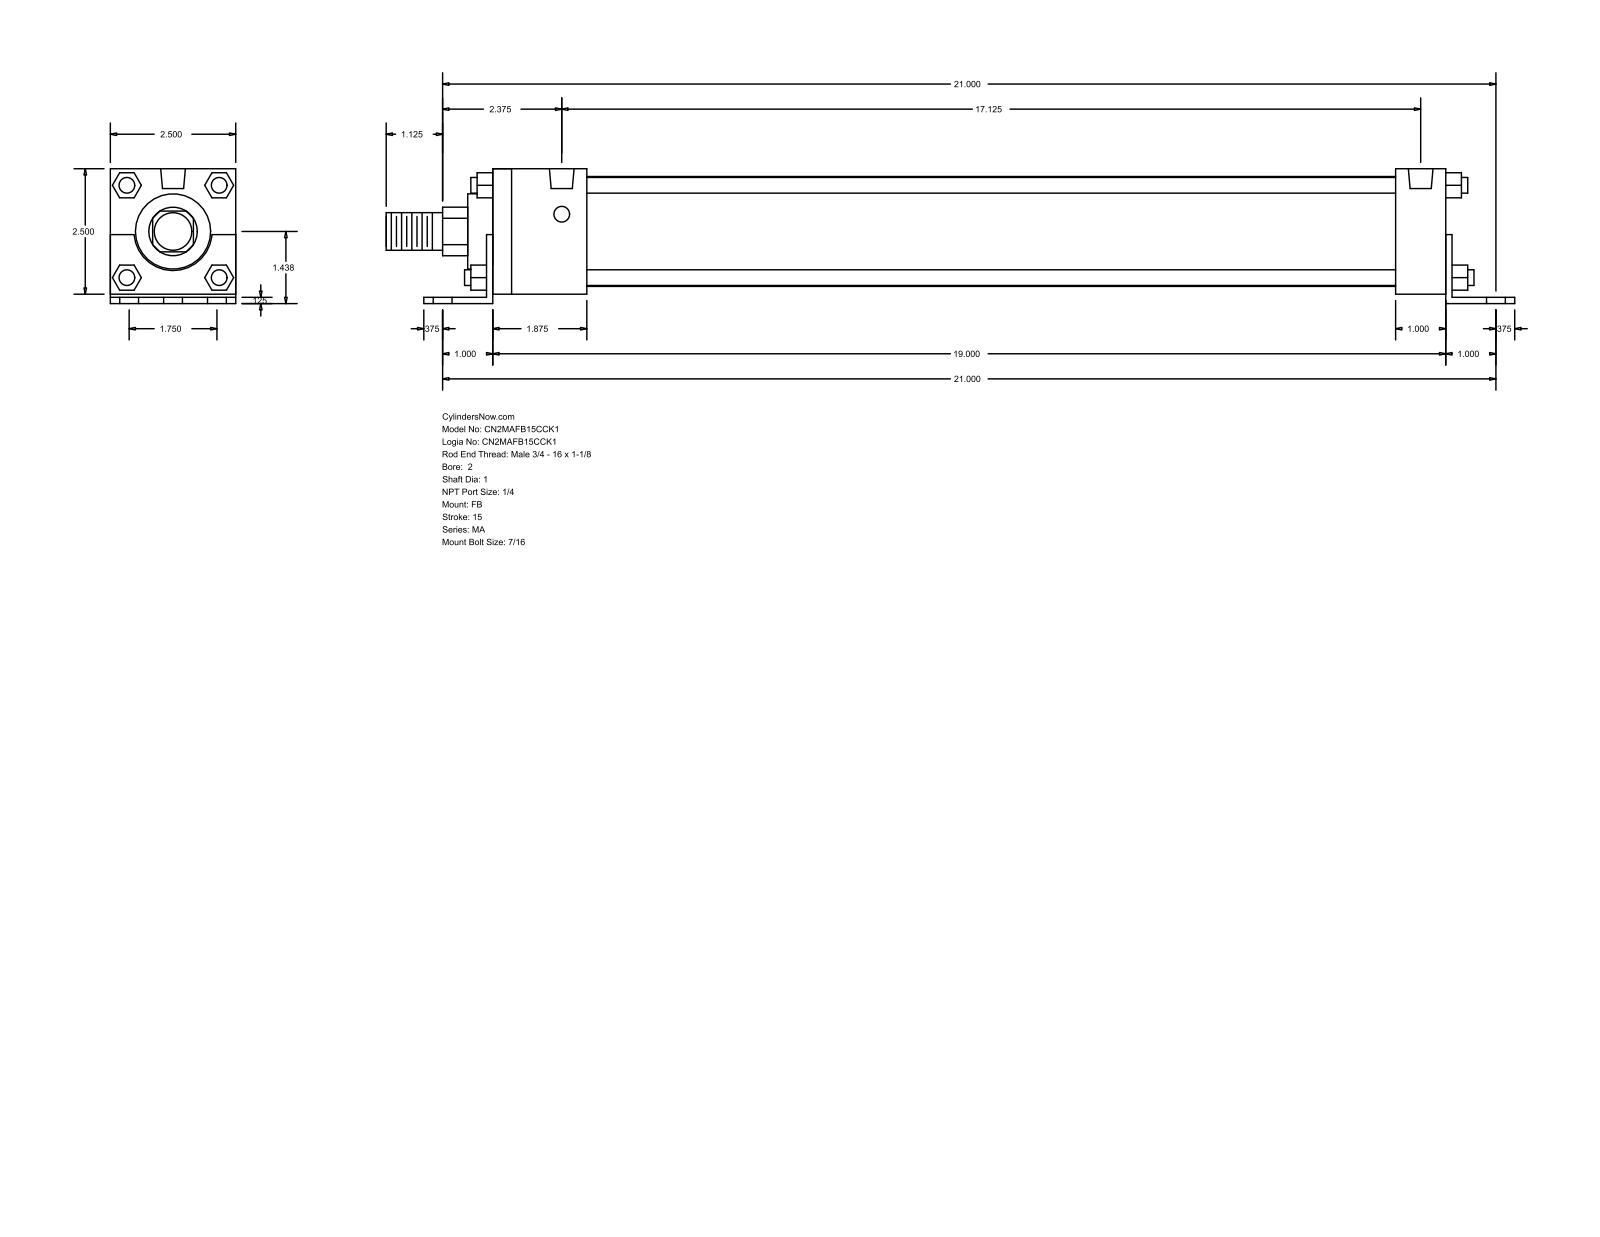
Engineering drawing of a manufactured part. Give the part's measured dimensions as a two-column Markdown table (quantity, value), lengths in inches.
| quantity | value |
| --- | --- |
| part name | MA_FB__0200_1 |
| STEP written by | GSSL Pune (CONFIG_CONTROL_DESIGN) |
| units | inches |
| bodies | 0 solids, 140 faces (105 planar, 35 cylindrical, 0 other) |
| overall size | 22.5 × 2.687 × 2.5 |
| round holes (diameter × count) | 0.437 × 6, 0.313 × 4, 0.492 × 2 |
| round bosses / shafts (diameter × count) | 0.313 × 4, 2.19 × 1, 1.5 × 1, 1 × 1, 0.75 × 1 |
| partial cylindrical surfaces (radius × count) | 0.484 × 1, 0.78 × 1 |
| main face-to-face distances | 2.5, 0.125, 0.187, 2.687, 0.063, 2.563, 0.5, 0.125, 19, 19.125 |
| hole center spacings | 0.875, 21.018, 21, 1.737, 1.75, 2.531, 17.125, 18.645 |
